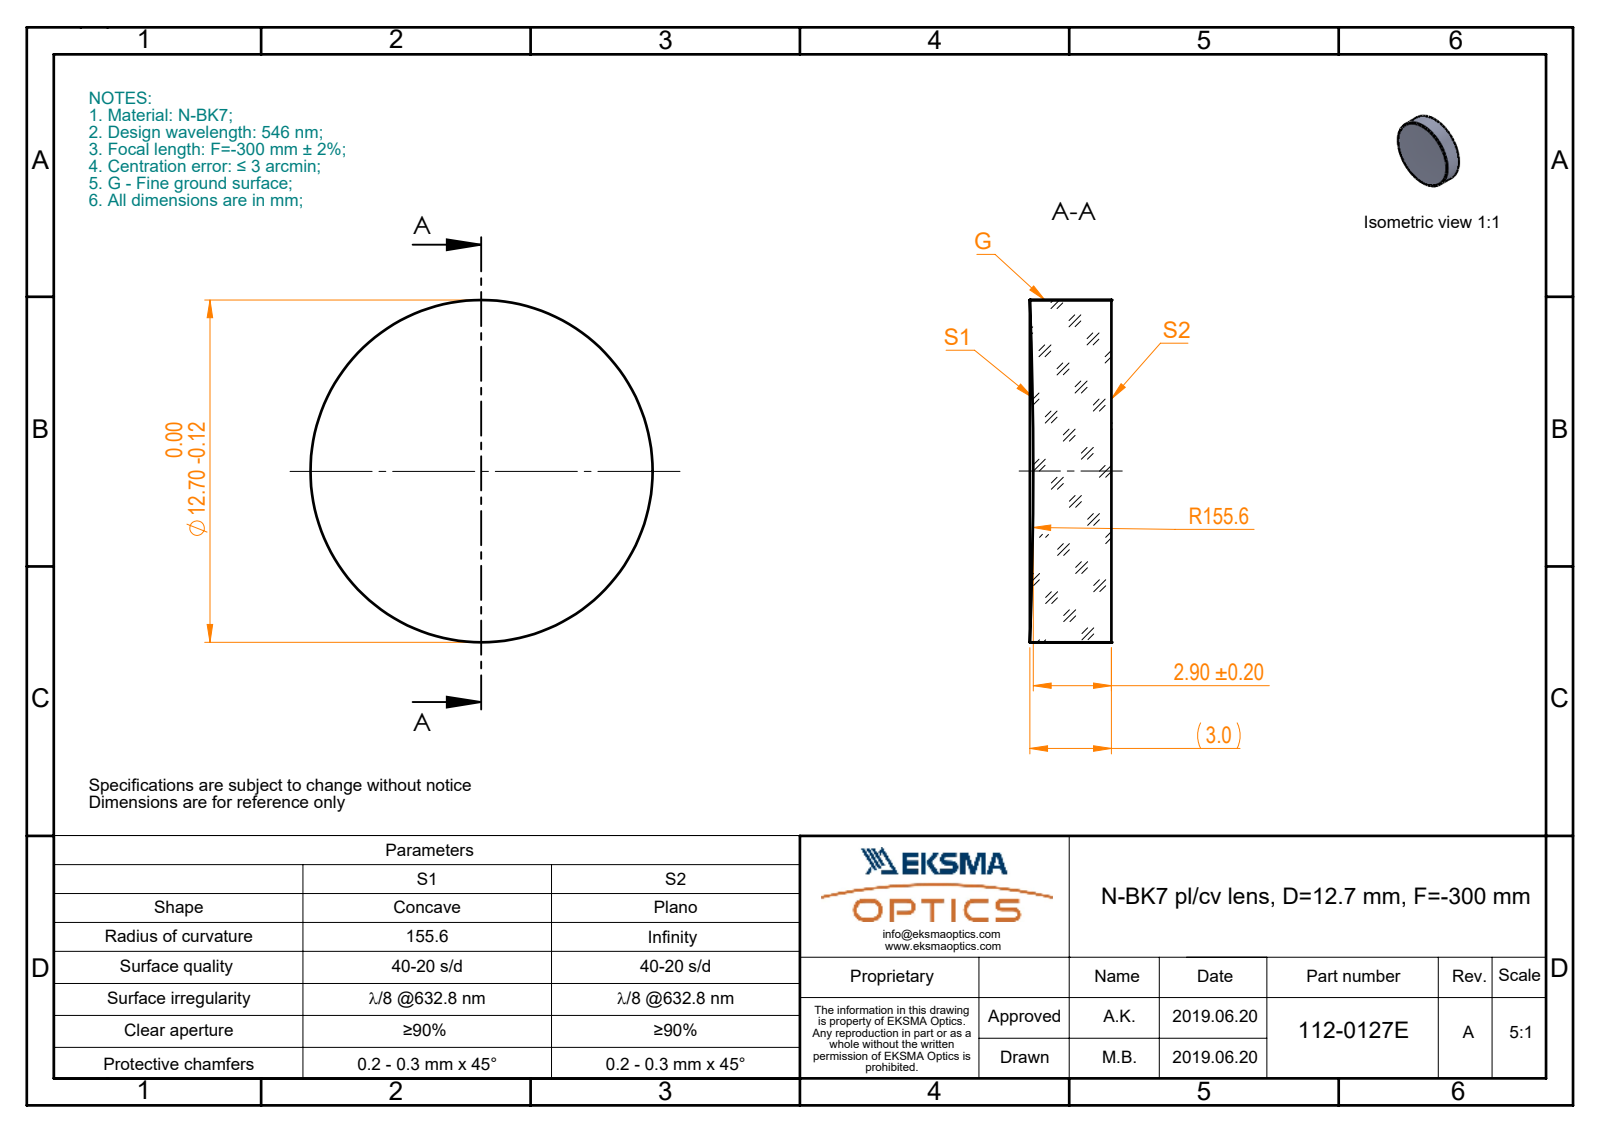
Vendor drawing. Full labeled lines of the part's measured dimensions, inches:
Part name (STEP PRODUCT): 112-0127E BK7 pl-cv 12.7 F-300
STEP written by: SolidWorks 2017 (CONFIG_CONTROL_DESIGN)
Units: inches
Bodies: 1 solid, 5 faces (1 planar, 2 cylindrical, 2 other)
Overall size (bounding box): 0.5 × 0.5 × 0.119
Volume: 0.023 in³ · Surface area: 0.58 in²
Round bosses / shafts (diameter × count): ⌀0.5 ×1
